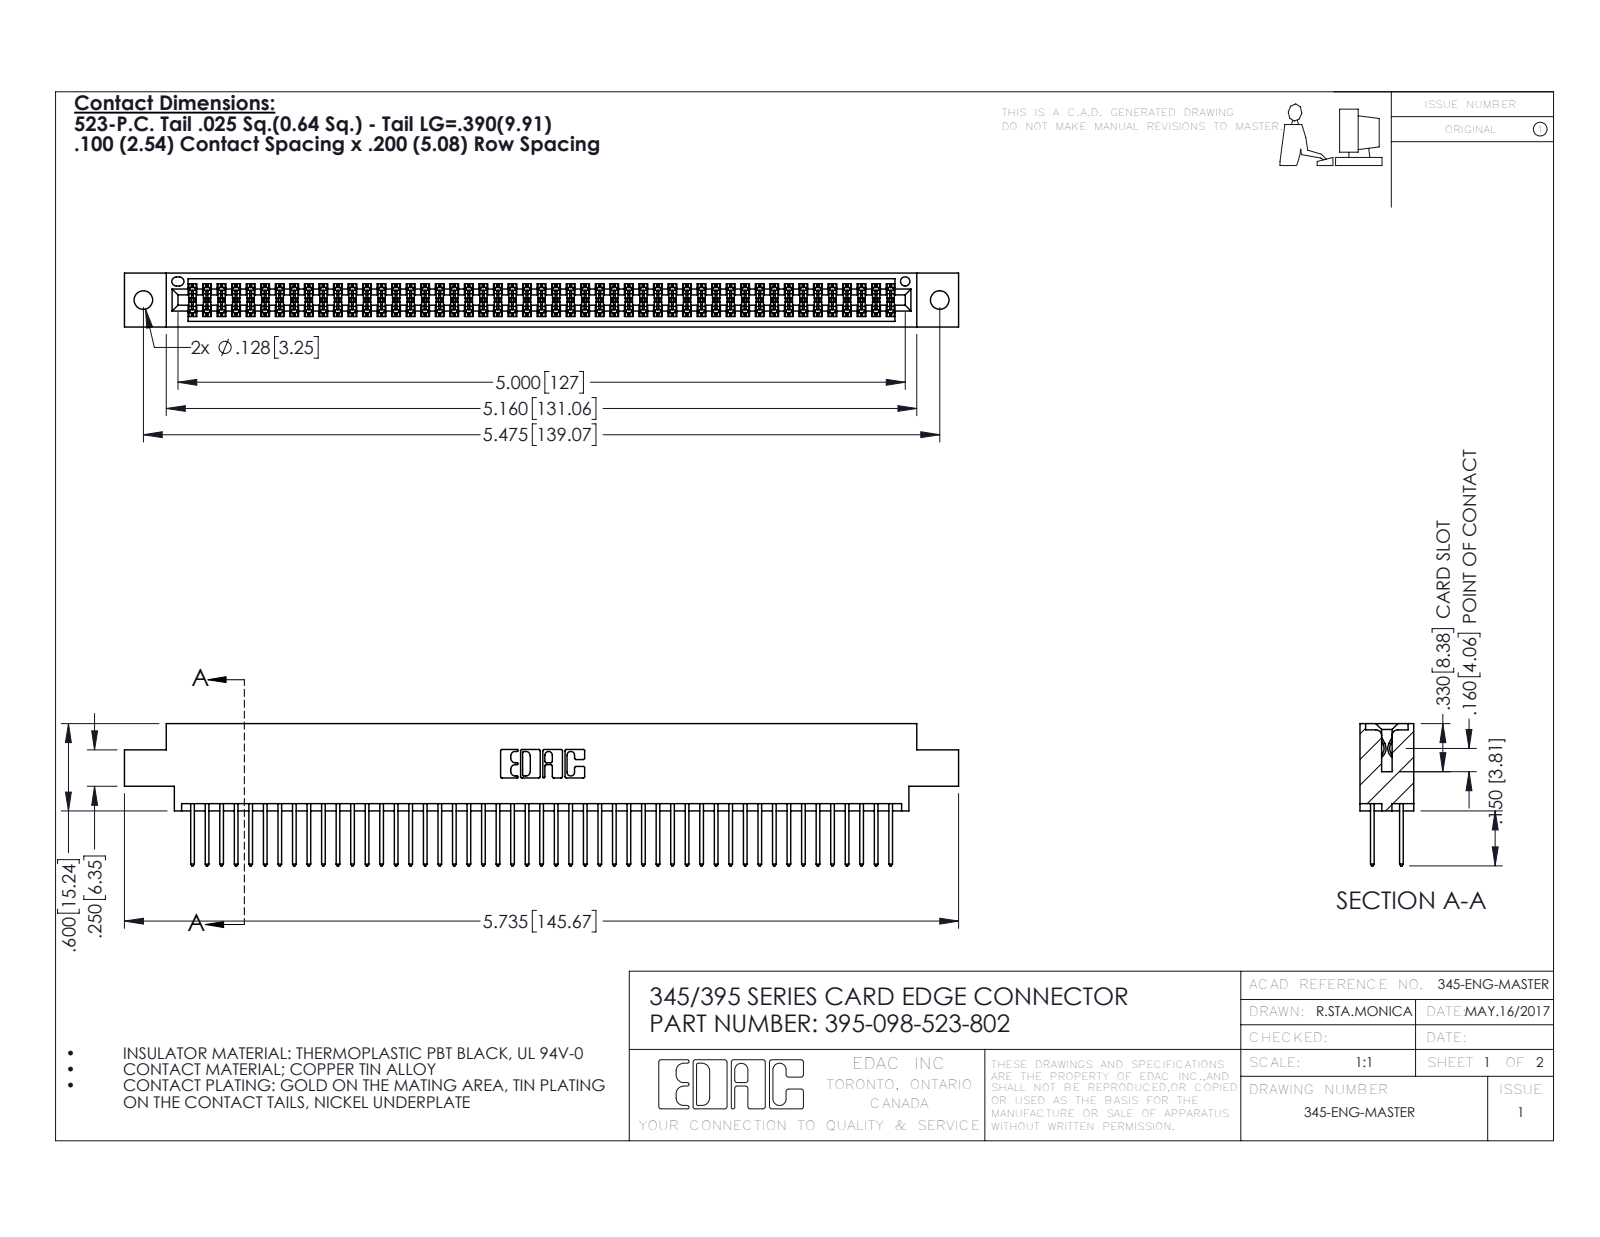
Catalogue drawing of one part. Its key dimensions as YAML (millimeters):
part_name: "345-292-001_345-293-123; 345 Part_0.170 Offset - 0.128 Dia; 395-098-523-802"
step_written_by: "SolidWorks 2016 (CONFIG_CONTROL_DESIGN)"
units: millimeters
bodies: {solids: 99, faces: 5030, planar: 3318, cylindrical: 1712, other: 0}
overall_size: [145.7, 24.8, 9.4]
volume: 14300
surface_area: 21990
round_holes:
  - {diameter: 3.3, count: 2}
  - {diameter: 1.6, count: 1}
partial_cylinders:
  - {radius: 0.2, count: 147}
  - {radius: 0.3, count: 98}
  - {radius: 0.3, count: 22}
  - {radius: 0.2, count: 6}
  - {radius: 0.8, count: 6}
  - {radius: 0.7, count: 3}
  - {radius: 0.4, count: 2}
  - {radius: 0.5, count: 2}
face_to_face_distances: [7.6, 1.8, 5.1, 2.5, 6.9, 0.6, 9.4, 5.7, 4.4, 3.8]
hole_center_spacings: [6.9, 133.1, 139.1]
